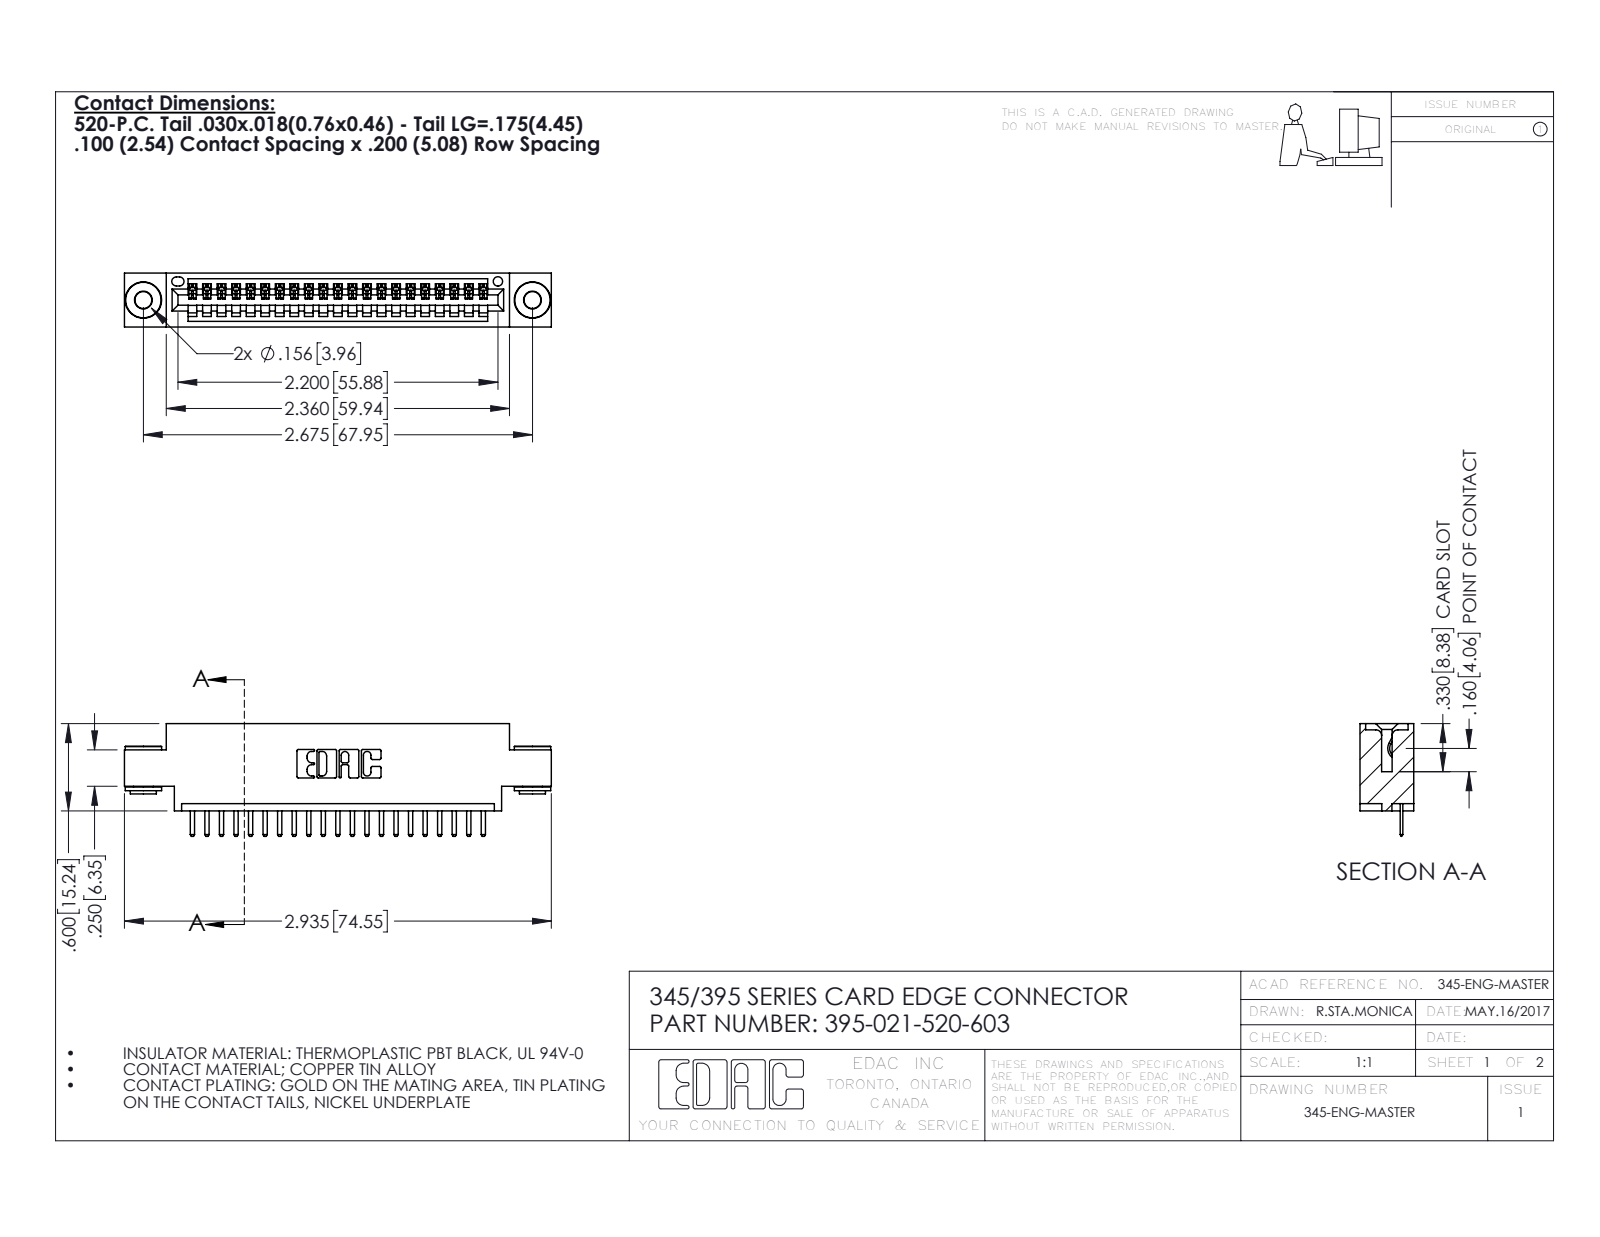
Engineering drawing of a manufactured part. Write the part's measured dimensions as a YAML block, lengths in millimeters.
part_name: "345 Part_0.170 Offset - 0.156 Dia-TH; 395-021-520-603; 345-292-001_345-293-120; 345-250-002_345-250-002-102"
step_written_by: "SolidWorks 2016 (CONFIG_CONTROL_DESIGN)"
units: millimeters
bodies: {solids: 24, faces: 1470, planar: 976, cylindrical: 486, other: 8}
overall_size: [74.5, 19.7, 9.4]
volume: 6750
surface_area: 8832
round_holes:
  - {diameter: 2.9, count: 2}
  - {diameter: 4, count: 2}
  - {diameter: 1.6, count: 1}
round_bosses_or_shafts:
  - {diameter: 6.4, count: 2}
  - {diameter: 4.6, count: 2}
  - {diameter: 3.5, count: 2}
partial_cylinders:
  - {radius: 0.3, count: 44}
  - {radius: 0.2, count: 42}
  - {radius: 0.3, count: 22}
  - {radius: 0.2, count: 6}
  - {radius: 0.8, count: 6}
  - {radius: 0.7, count: 3}
  - {radius: 0.8, count: 2}
  - {radius: 1, count: 2}
face_to_face_distances: [9.4, 1.8, 7.6, 5.1, 2.5, 6.9, 0.6, 5.7, 4.4, 1.8]
hole_center_spacings: [6.9, 62, 67.9]
